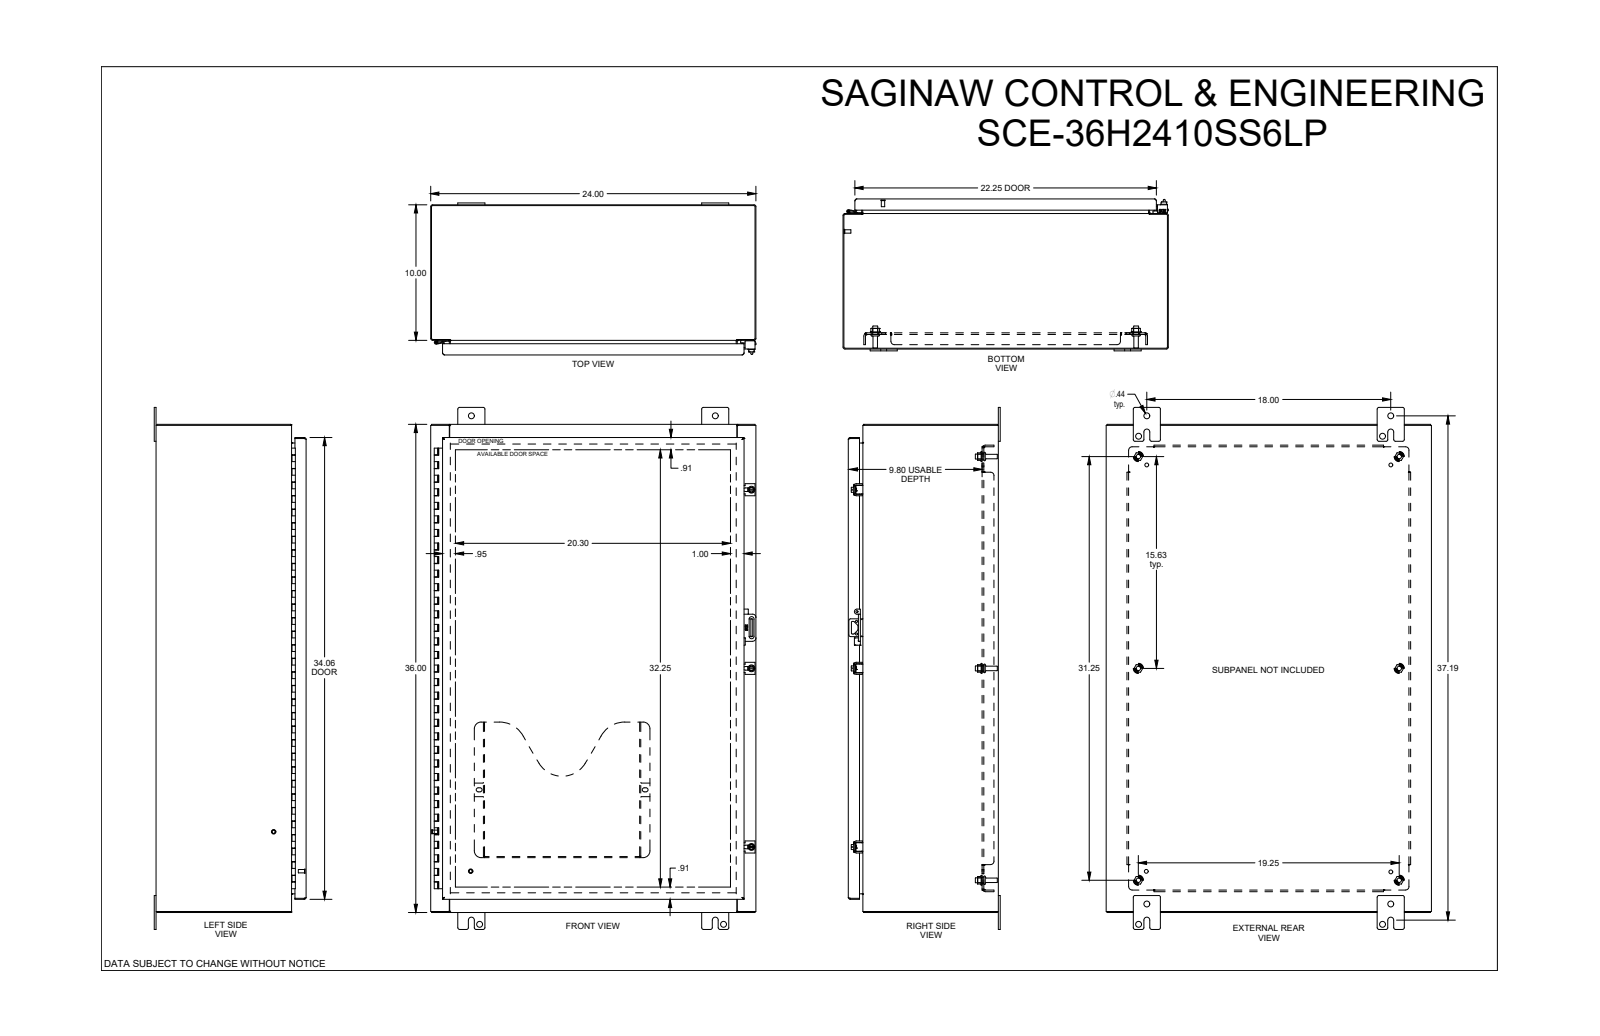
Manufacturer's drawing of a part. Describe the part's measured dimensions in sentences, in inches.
The part is named "SCE-36H2410SS6LP". Its 3-D file was written by "SolidWorks 2019 (CONFIG_CONTROL_DESIGN)". It is 0 solids with 4019 faces: 1647 planar, 844 cylindrical and 1528 other. Overall it measures 38.5 by 24 by 11.208 inches. Round holes: 8 of diameter 0.437, 6 of diameter 0.25, 6 of diameter 0.367, 6 of diameter 0.5, 5 of diameter 0.19, 5 of diameter 0.193, 4 of diameter 0.281, 3 of diameter 0.203, 2 of diameter 0.16, 1 of diameter 0.13, 1 of diameter 0.132. Round bosses or shafts: 8 of diameter 0.248, 6 of diameter 0.563, 6 of diameter 0.366, 6 of diameter 0.332, 5 of diameter 0.256, 5 of diameter 0.188, 4 of diameter 0.25, 3 of diameter 0.507. Partial cylindrical surfaces (rounded edges, fillets, slot ends): 160 of radius 0.01, 44 of radius 0.015, 36 of radius 0.029, 29 of radius 0.06, 27 of radius 0.03, 27 of radius 0.125, 22 of radius 0.04, 14 of radius 0.07. The main face-to-face distances are 0.075, 0.075, 10.998, 10.923, 1.2, 9.873, 11.073, 10.998, 23.925, 9.923. The hole center spacings are 1.619, 18, 36, 40.249, 0.515, 7.875, 7.875, 15.019.
